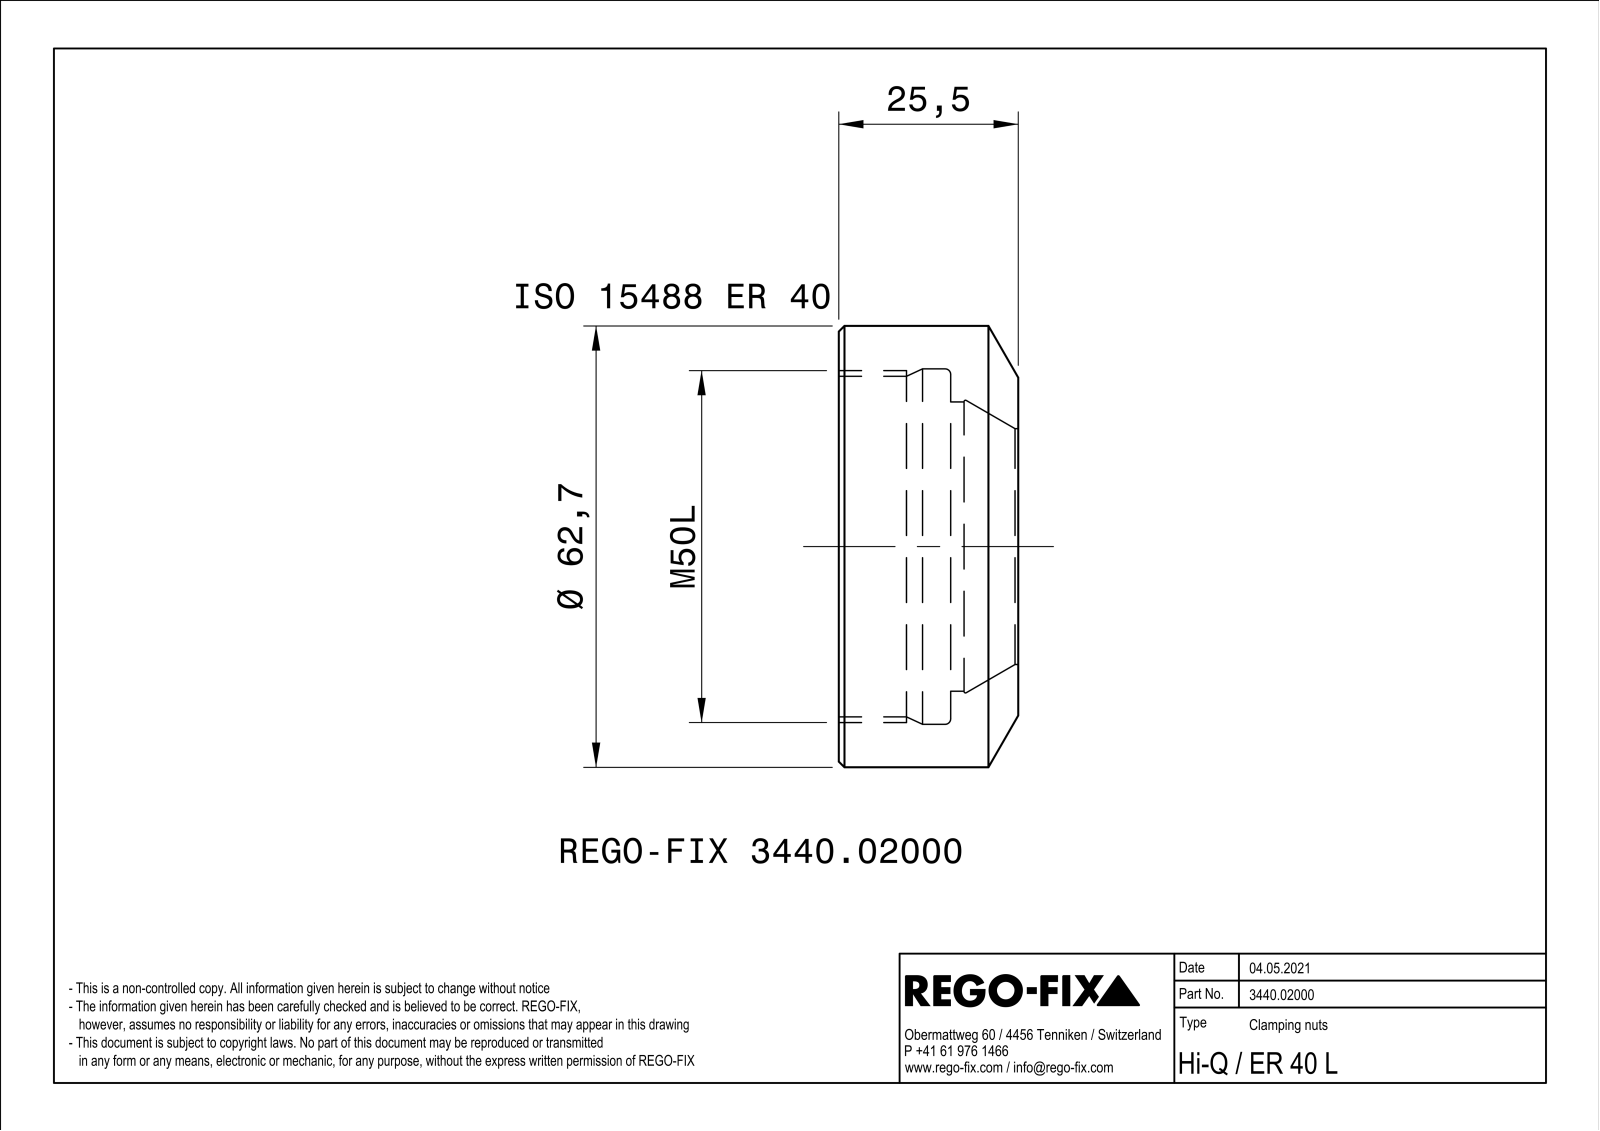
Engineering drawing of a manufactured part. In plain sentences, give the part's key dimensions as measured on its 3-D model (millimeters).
The part is named "NOCUT". Its 3-D file was written by "SIEMENS PLM Software Solid Edge ST10 (AUTOMOTIVE_DESIGN)". It is 1 solid with 81 faces: 46 planar, 5 cylindrical and 30 other. Overall it measures 62.7 by 62.7 by 25.5 millimeters. Its volume is 33 626 cubic millimeters and its surface area 12 406 square millimeters. Round holes: 1 of diameter 33.5, 1 of diameter 41, 1 of diameter 48.38, 1 of diameter 50.5. Round bosses or shafts: 1 of diameter 62.7. The main face-to-face distances are 25.5, 9.6, 15.9, 57, 10.3, 10.32, 42.88, 47.12, 42.92, 47.1.
